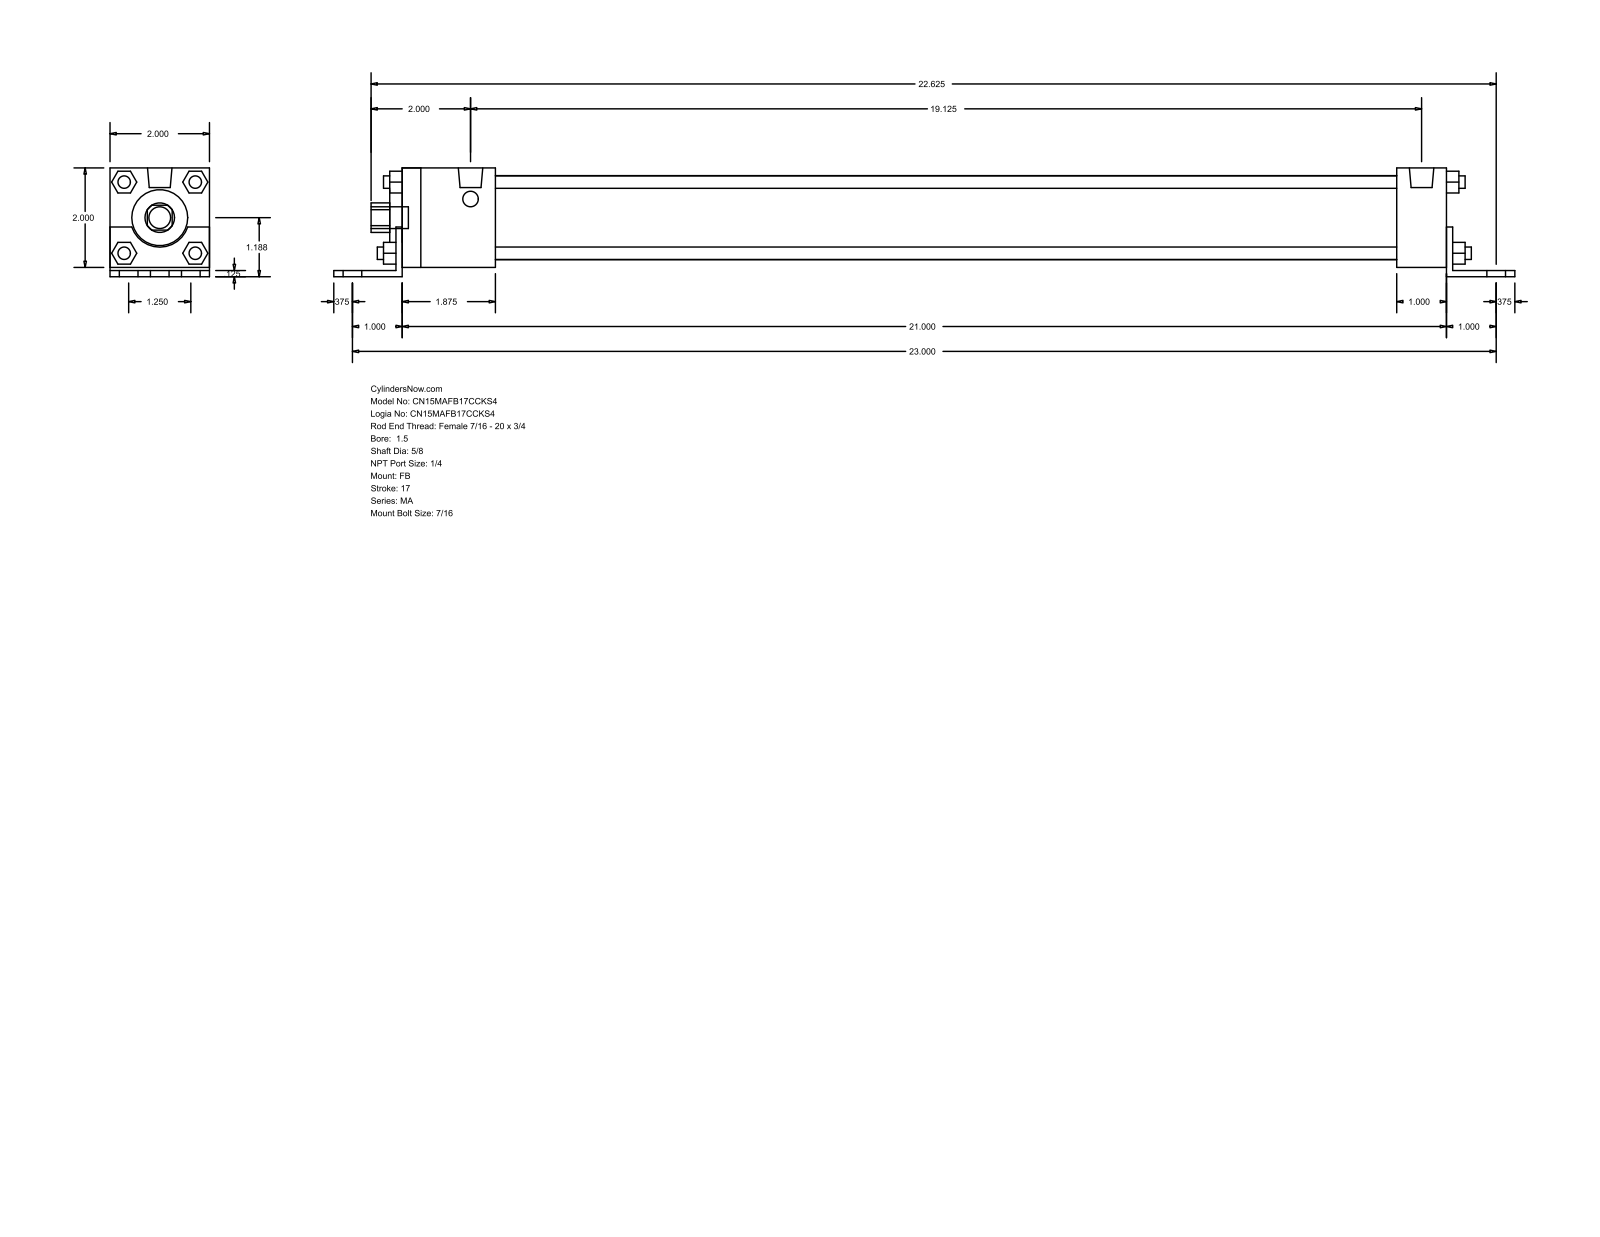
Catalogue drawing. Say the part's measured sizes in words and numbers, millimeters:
The part is named "MA_FB__0150_0.625". Its 3-D file was written by "GSSL Pune (CONFIG_CONTROL_DESIGN)". It is 0 solids with 140 faces: 105 planar, 35 cylindrical and 0 other. Overall it measures 603.25 by 55.56 by 50.8 millimeters. Round holes: 1 of diameter 15.88, 1 of diameter 28.57, 1 of diameter 42.93. Round bosses or shafts: 7 of diameter 11.11, 4 of diameter 7.94, 4 of diameter 6.35, 2 of diameter 12.49. Partial cylindrical surfaces (rounded edges, fillets, slot ends): 1 of radius 7.54, 1 of radius 15.05. The main face-to-face distances are 50.8, 3.17, 4.76, 55.56, 1.59, 52.39, 3.18, 536.57, 6.35, 542.92.
